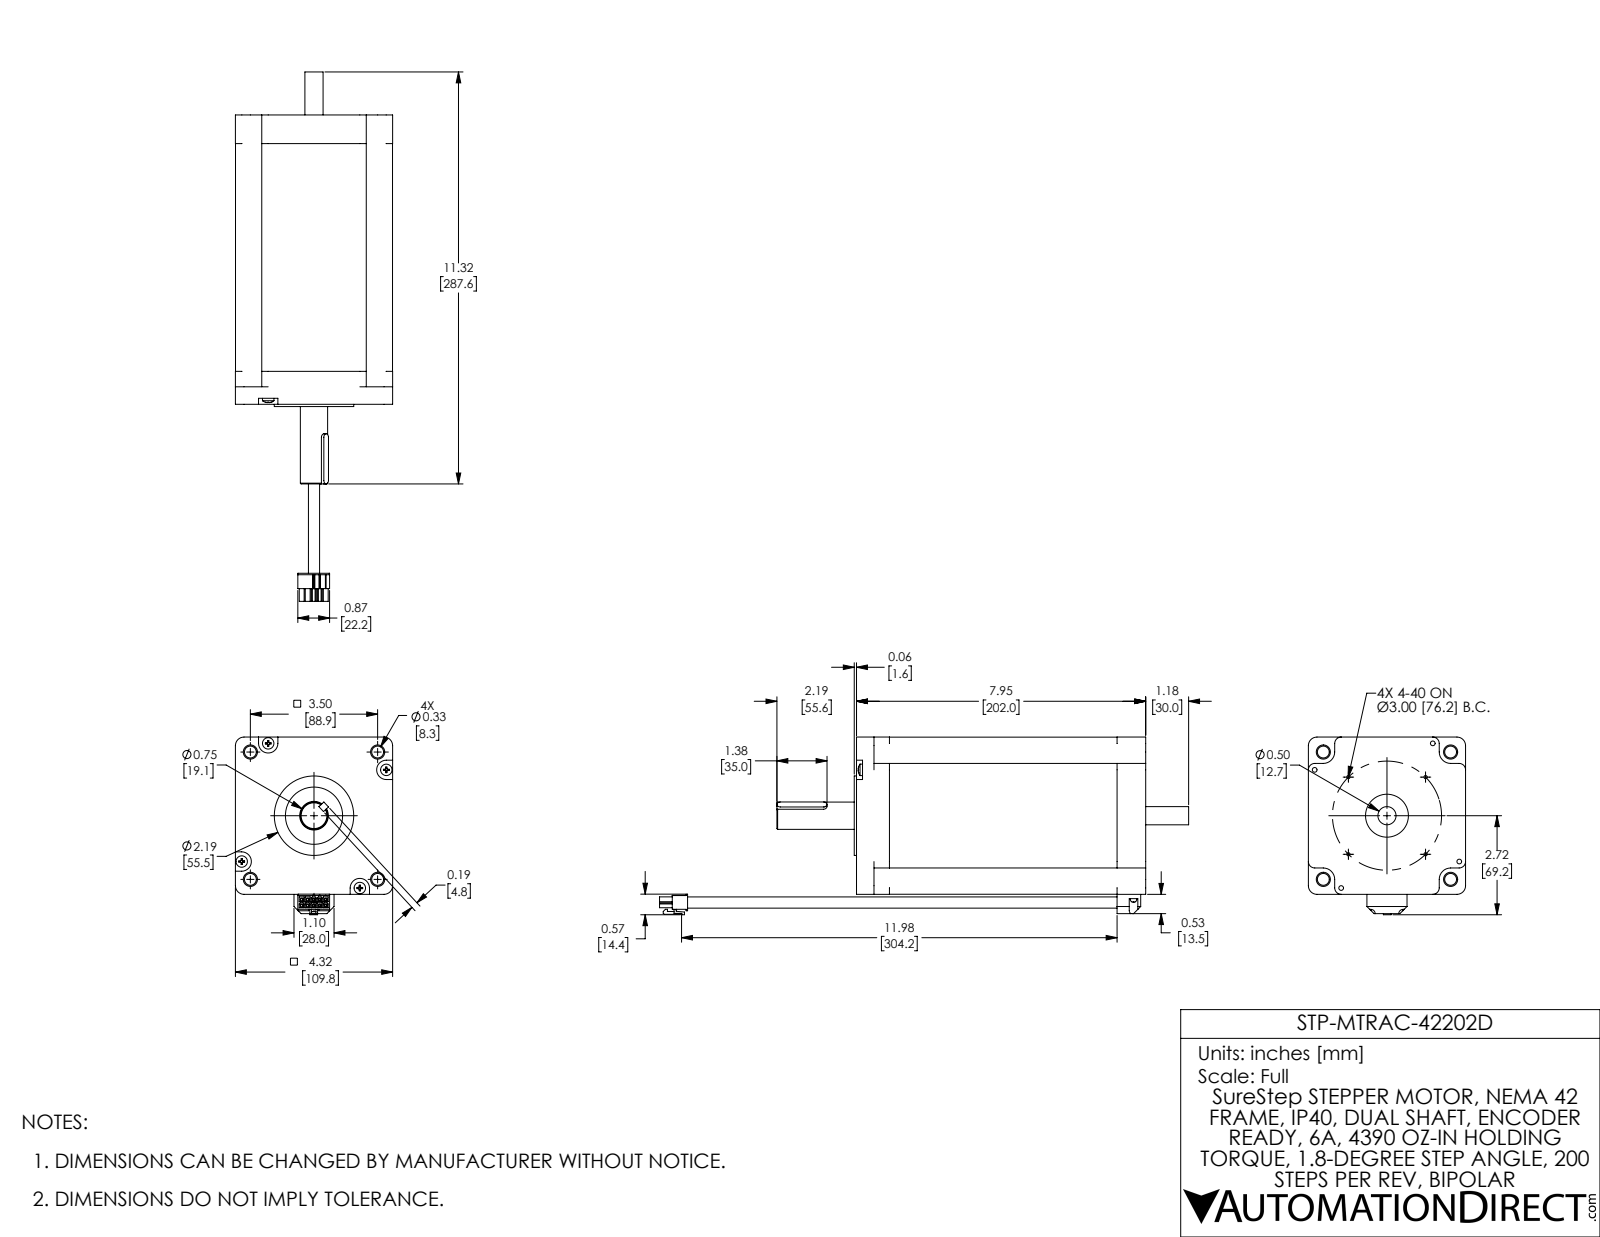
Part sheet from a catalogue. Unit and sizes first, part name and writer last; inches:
Units: inches
Overall size (bounding box): 14.551 × 4.884 × 4.323
Round holes (diameter × count): ⌀0.177 ×8, ⌀0.13 ×6, ⌀0.181 ×4, ⌀0.327 ×4, ⌀0.591 ×1, ⌀0.787 ×1, ⌀1.116 ×1, ⌀1.181 ×1, ⌀1.378 ×1, ⌀1.575 ×1, ⌀1.627 ×1, ⌀2.047 ×1
Round bosses / shafts (diameter × count): ⌀0.315 ×4, ⌀0.157 ×4, ⌀0.177 ×2, ⌀2.579 ×1, ⌀2.559 ×1, ⌀2.186 ×1, ⌀1.207 ×1, ⌀1 ×1
Partial cylindrical surfaces — rounded edges, fillets, slot ends (radius × count): R0.012 ×22, R0.177 ×16, R0.01 ×6, R0.236 ×4, R0.266 ×4, R0.315 ×4, R0.094 ×2, R0.118 ×2
Main face-to-face distances: 4.319, 4.321, 0.669, 0.724, 3.598, 0.722, 3.596, 7.953, 6.87, 0.787
Hole centre spacings: 0.545, 2.354, 3.019, 3.329, 3.77, 4.799, 1.03, 2.475
Volume: 64.45 in³ · Surface area: 423 in²
Bodies: 13 solids, 1000 faces (603 planar, 207 cylindrical, 190 other)
Part name (STEP PRODUCT): STP-MTRAC-42202D
STEP written by: SolidWorks 2017 (AUTOMOTIVE_DESIGN)
